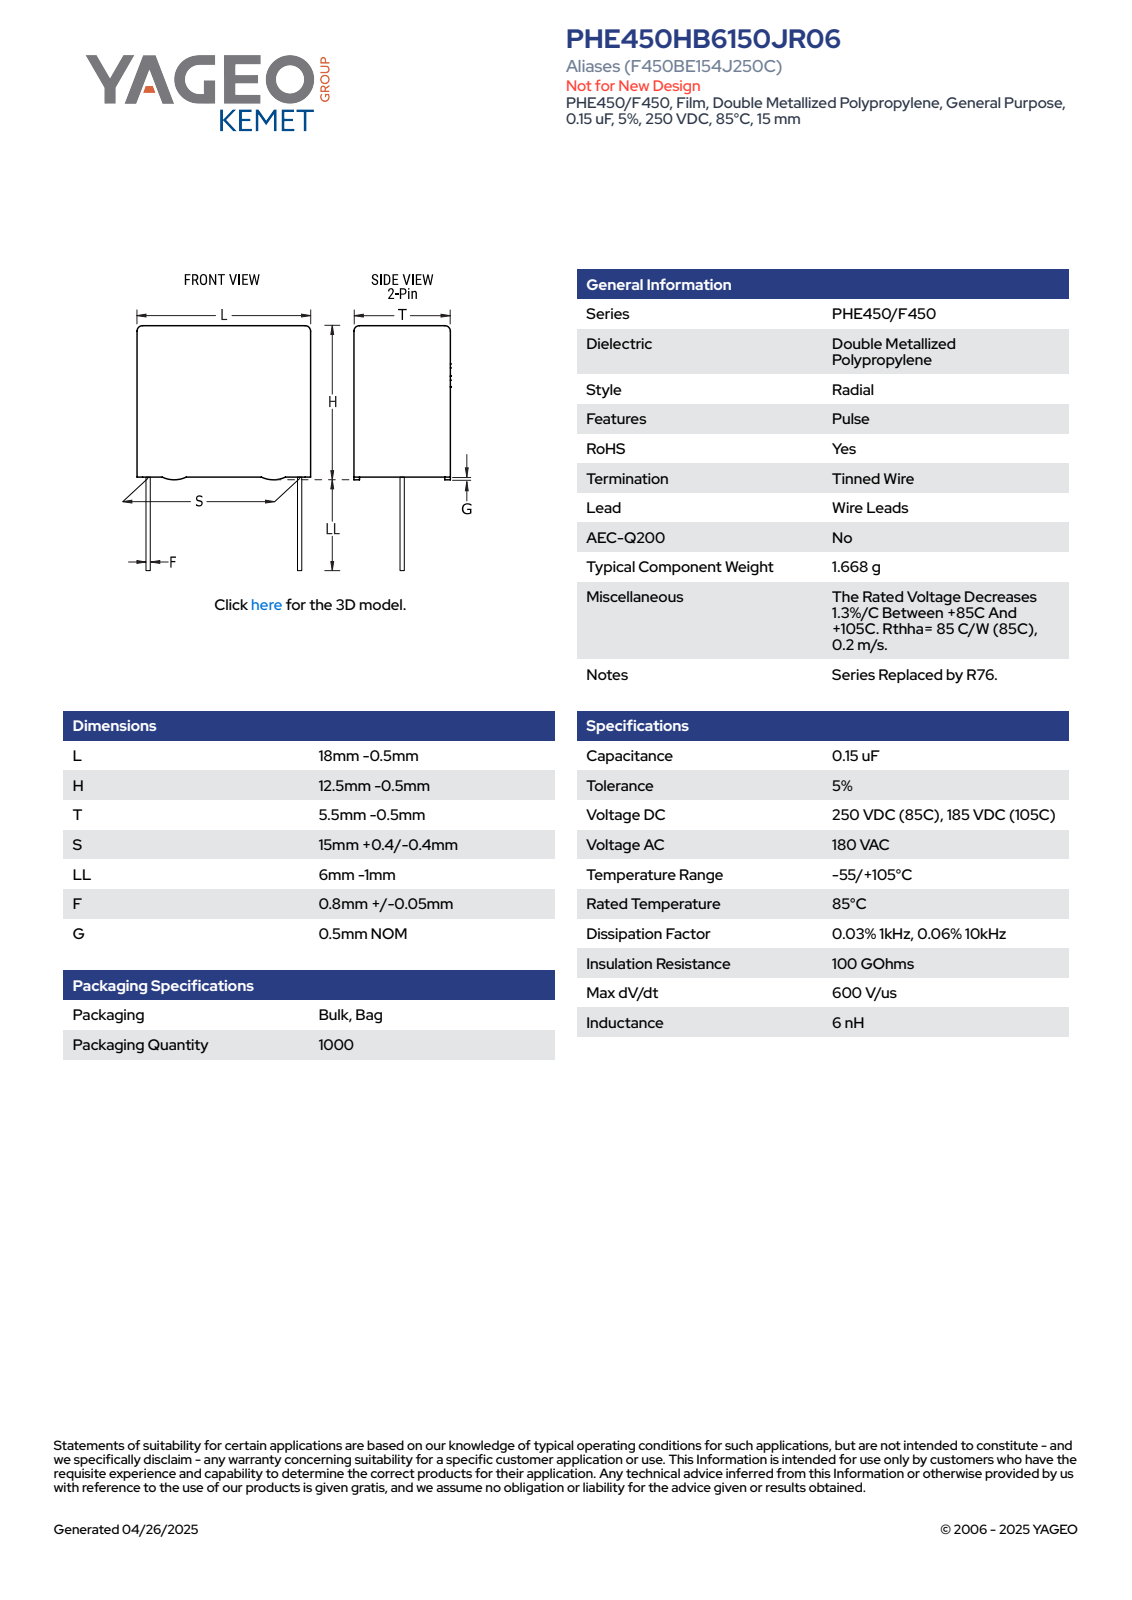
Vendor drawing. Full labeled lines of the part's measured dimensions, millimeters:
Part name (STEP PRODUCT): CFR_RBG_18X12.5X5.5_L17.5H12T5S15LL5F0.85G0.5
STEP written by: SolidWorks 2021 (AUTOMOTIVE_DESIGN)
Units: millimetres
Bodies: 4 solids, 89 faces (81 planar, 8 cylindrical, 0 other)
Overall size (bounding box): 17.5 × 17 × 5
Volume: 1 012 mm³ · Surface area: 757 mm²
Round bosses / shafts (diameter × count): ⌀0.85 ×2
Partial cylindrical surfaces — rounded edges, fillets, slot ends (radius × count): R0.5 ×4
Main face-to-face distances: 5, 11.5, 17.5, 0.5, 12, 4.72, 4.43, 4.71, 5.5, 17
